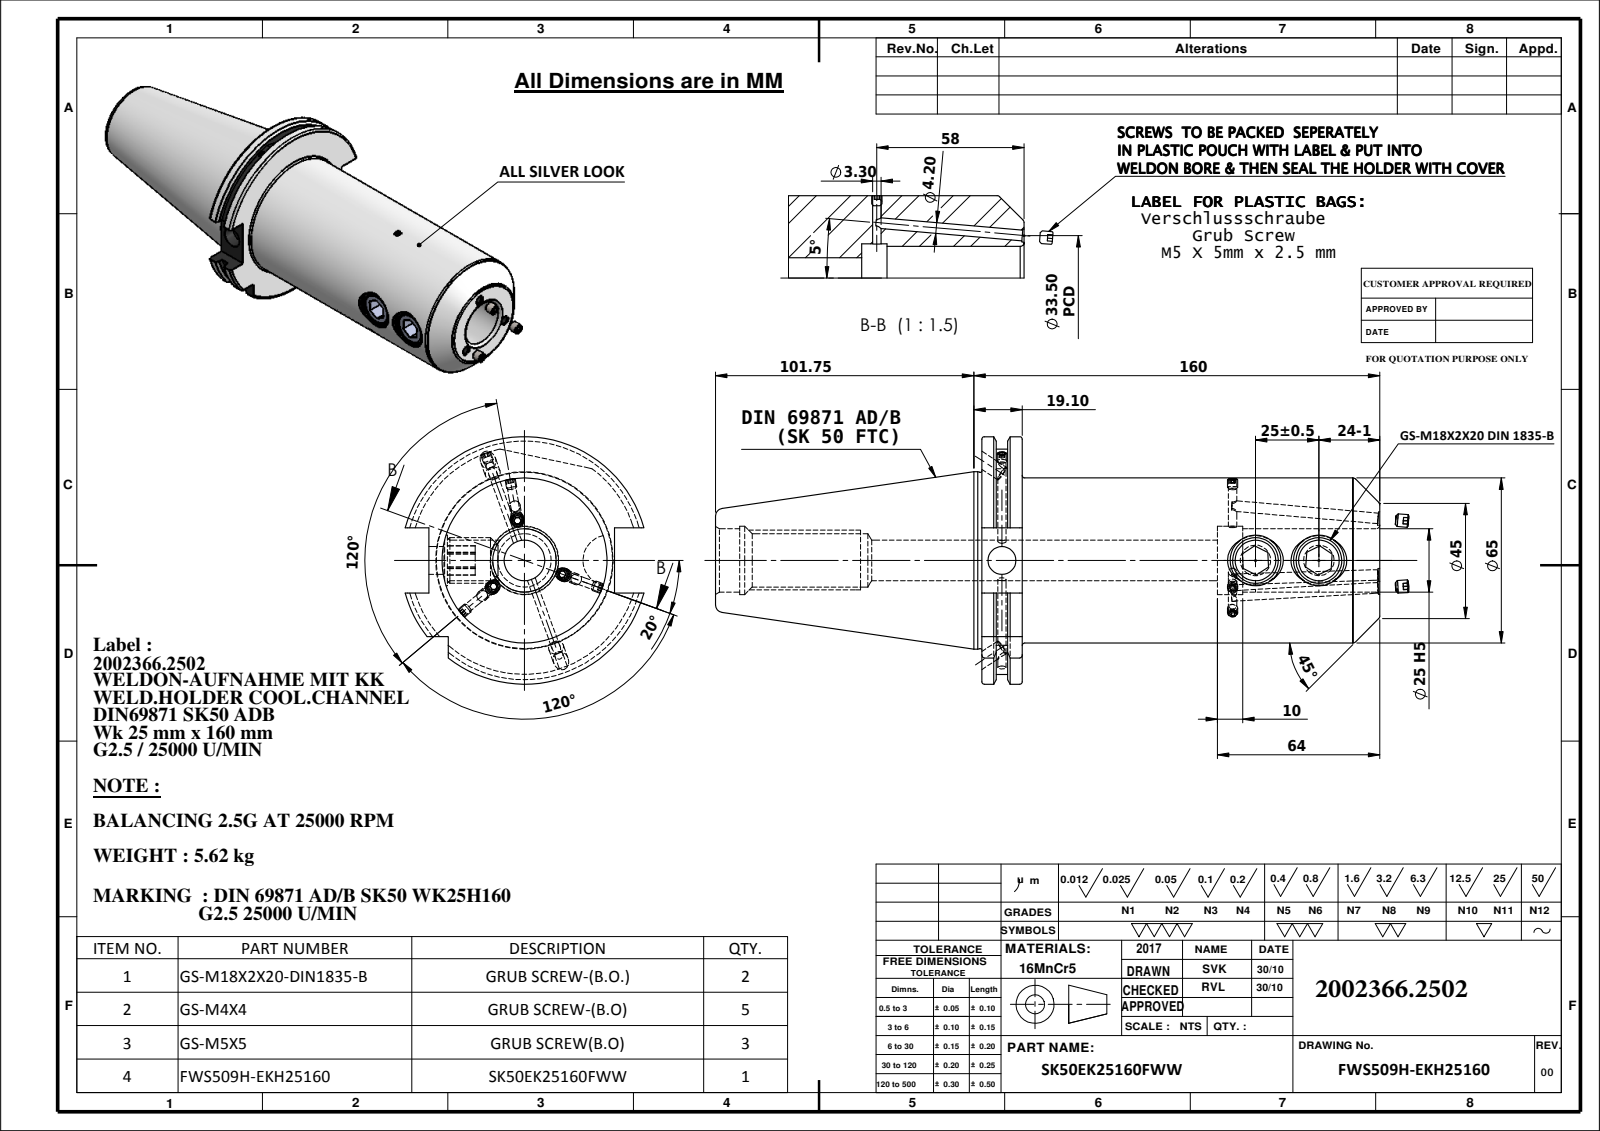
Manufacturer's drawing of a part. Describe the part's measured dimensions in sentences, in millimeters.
The part is named "Copy of M4X4_DIN 913 - M4 x 4-N; GS-M18X2X20; M5X5_DIN 913 - M5 x 5-N; SK50EK25160FWW (+1 more)". Its 3-D file was written by "SolidWorks 2009 (CONFIG_CONTROL_DESIGN)". It is 10 solids with 299 faces: 117 planar, 92 cylindrical and 90 other. Overall it measures 273.19 by 97.5 by 94.05 millimeters. Its volume is 730 205 cubic millimeters and its surface area 89 362 square millimeters. Round holes: 4 of diameter 3.3, 3 of diameter 4.2, 3 of diameter 5.2, 3 of diameter 16, 2 of diameter 6, 2 of diameter 20, 1 of diameter 11, 1 of diameter 21, 1 of diameter 25, 1 of diameter 27. Round bosses or shafts: 4 of diameter 4, 3 of diameter 5, 2 of diameter 18, 1 of diameter 69.85, 1 of diameter 69.45, 1 of diameter 65. Partial cylindrical surfaces (rounded edges, fillets, slot ends): 1 of radius 44.9, 1 of radius 48.75. The main face-to-face distances are 15.9, 156.8, 140.9, 10.15, 5.75, 146.65, 5.66, 4.49, 10.24, 151.14. The hole center spacings are 25, 99.9, 124.9.
